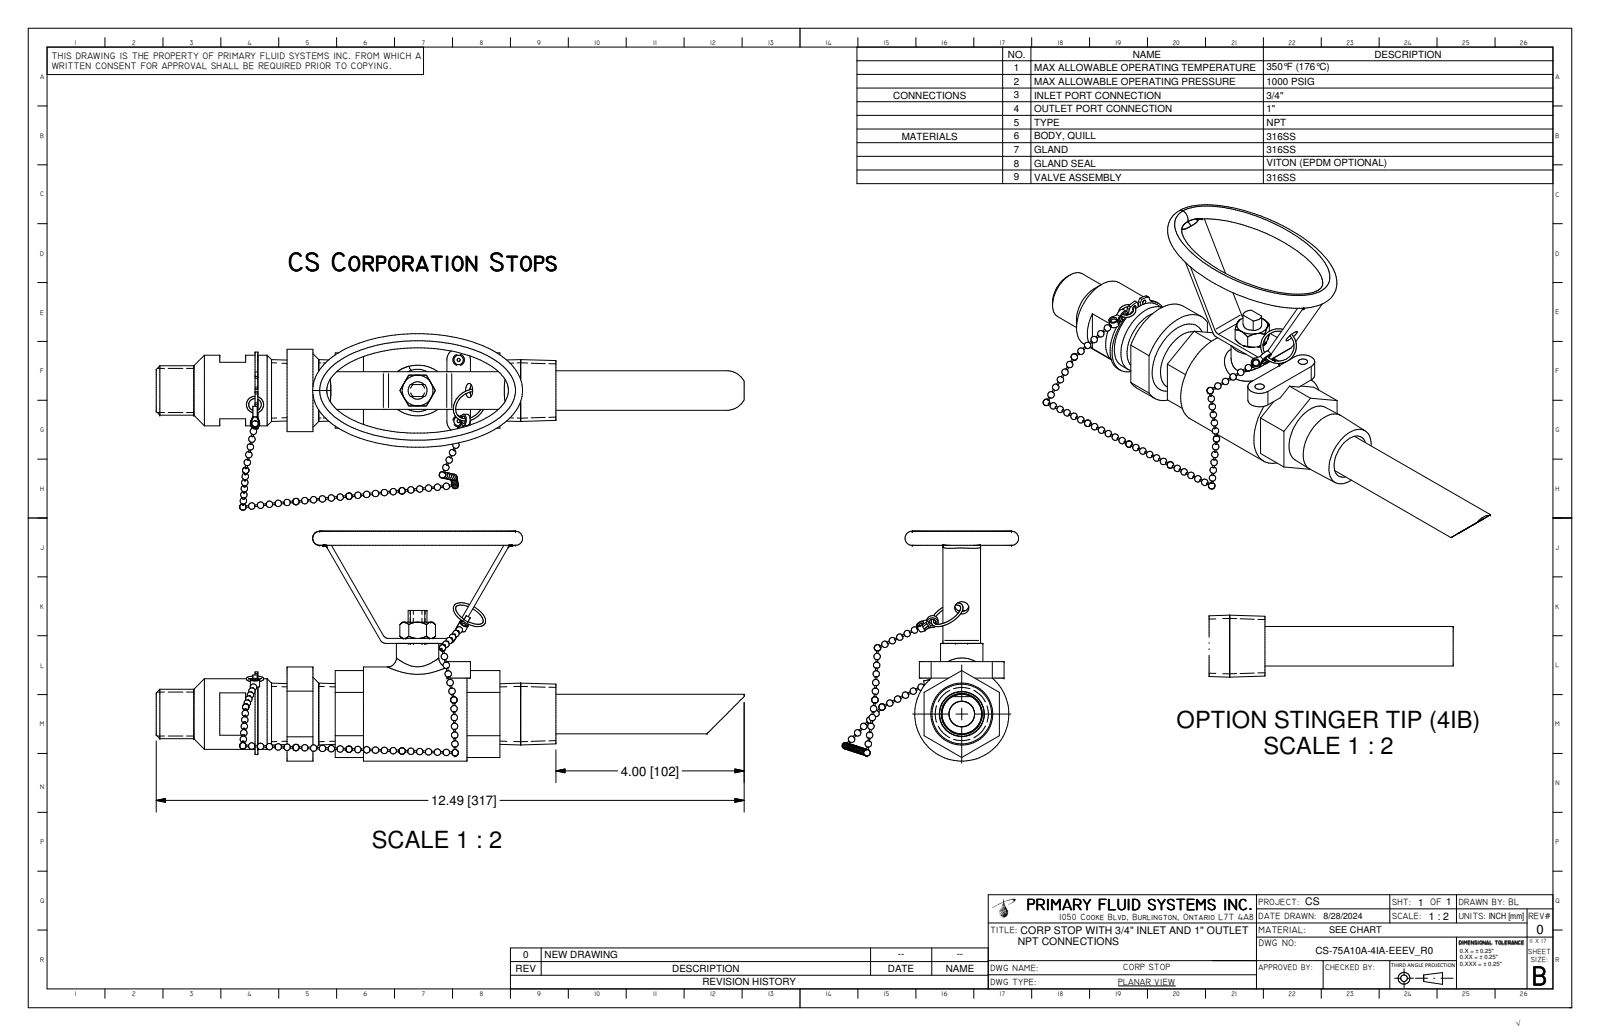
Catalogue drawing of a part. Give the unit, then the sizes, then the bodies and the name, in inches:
Units: inches
Overall size (bounding box): 12.493 × 4.882 × 3.747
Round holes (diameter × count): ⌀0.067 ×2, ⌀0.098 ×2, ⌀0.15 ×2, ⌀0.157 ×2, ⌀0.2 ×2, ⌀0.3 ×1, ⌀0.37 ×1, ⌀0.54 ×1, ⌀0.546 ×1, ⌀0.875 ×1, ⌀0.957 ×1, ⌀0.984 ×1
Round bosses / shafts (diameter × count): ⌀0.035 ×9, ⌀0.236 ×2, ⌀2 ×1, ⌀1.634 ×1, ⌀1.5 ×1, ⌀1.33 ×1, ⌀1.128 ×1, ⌀1.05 ×1
Partial cylindrical surfaces — rounded edges, fillets, slot ends (radius × count): R0.125 ×6, R0.054 ×2, R0.098 ×2, R0.197 ×2, R0.25 ×2, R0.2 ×1, R0.898 ×1
Main face-to-face distances: 0.104, 1.6, 0.2, 1.2, 4.525, 0.475, 0.4, 2.305, 0.25, 1.025
Hole centre spacings: 0.795, 1.088, 0.295, 0.314, 0.606, 0.708, 0.844, 1.3
Volume: 17.51 in³ · Surface area: 163.7 in²
Bodies: 21 solids, 330 faces (125 planar, 107 cylindrical, 98 other)
STEP written by: Autodesk Inventor 2025 (CONFIG_CONTROL_DESIGN)
